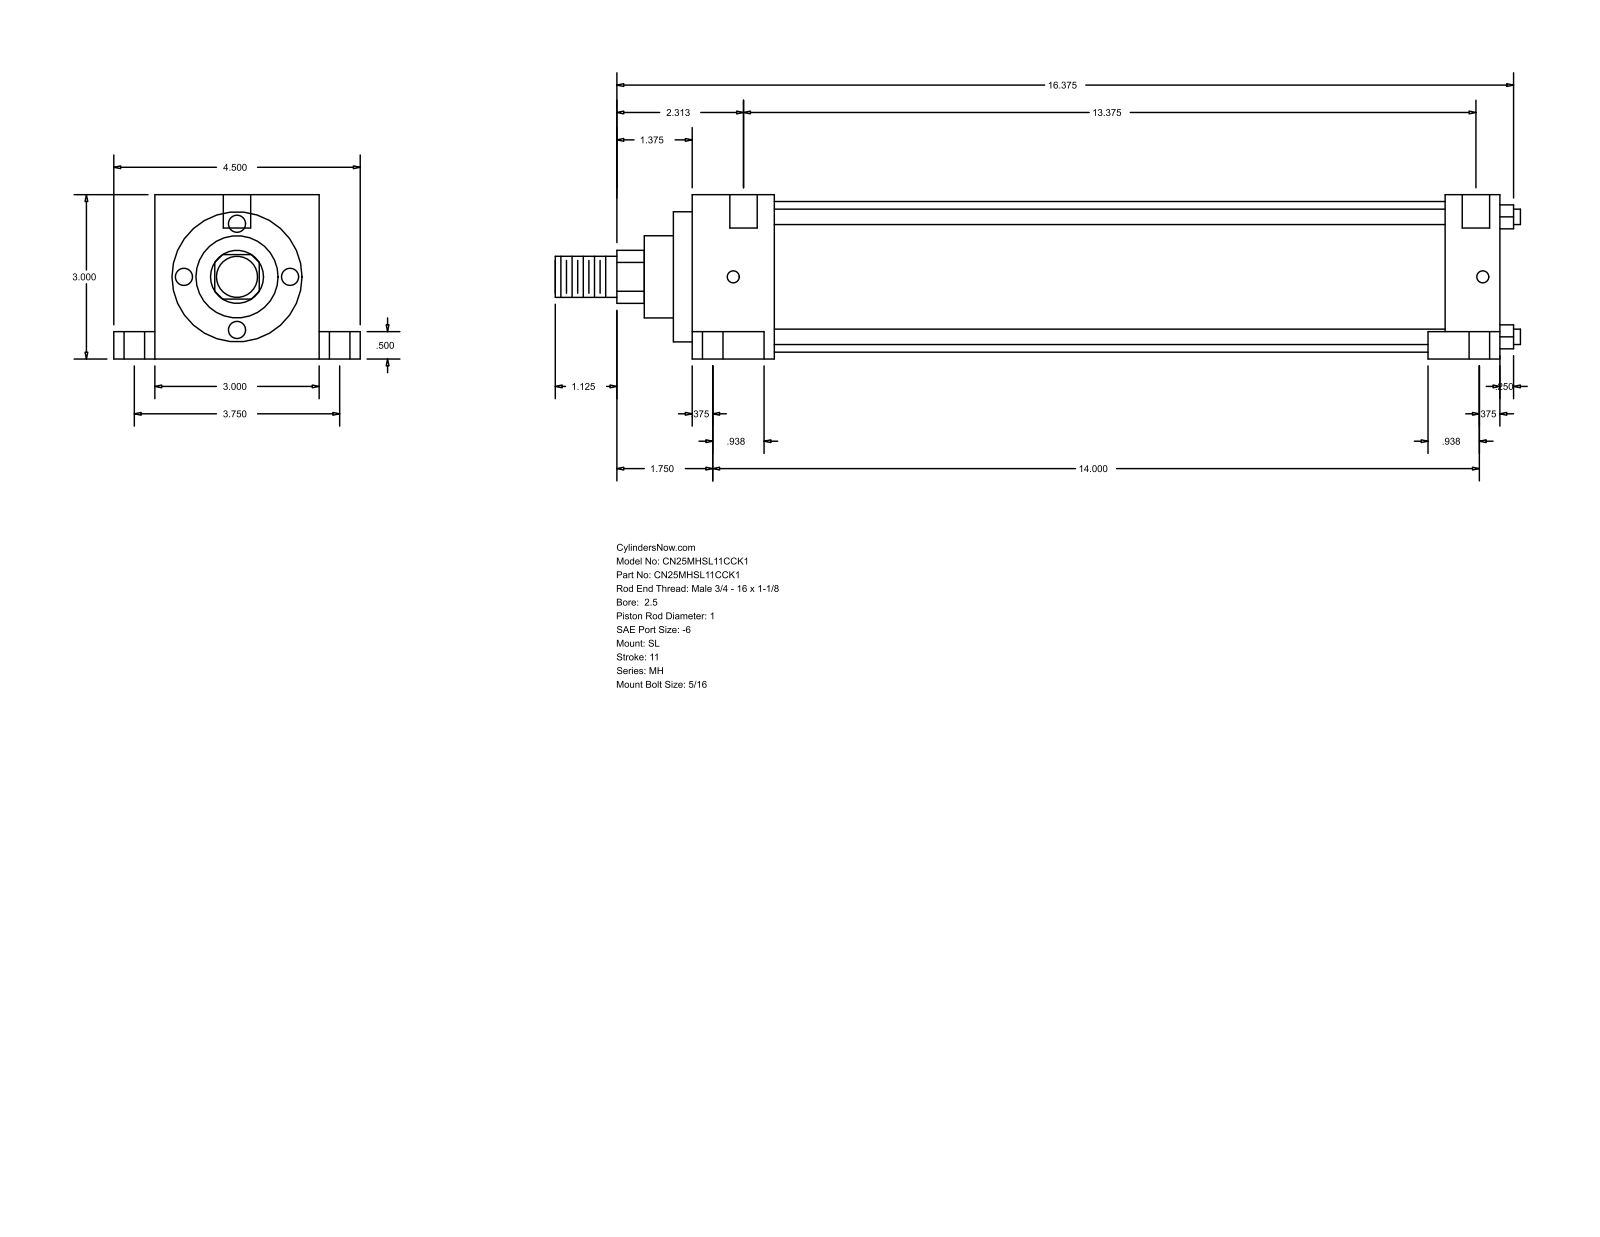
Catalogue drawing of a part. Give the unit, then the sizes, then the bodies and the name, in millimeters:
Units: millimetres
Overall size (bounding box): 447.68 × 114.3 × 76.2
Round holes (diameter × count): ⌀5.56 ×2, ⌀9.53 ×2, ⌀15.88 ×2, ⌀12.7 ×1
Round bosses / shafts (diameter × count): ⌀7.14 ×4, ⌀69.85 ×1, ⌀60.33 ×1, ⌀38.1 ×1, ⌀25.4 ×1, ⌀19.05 ×1
Partial cylindrical surfaces — rounded edges, fillets, slot ends (radius × count): R12.29 ×1
Main face-to-face distances: 76.2, 25.39, 357.99, 383.38, 12.7, 63.5, 19.05, 95.25, 13.49, 371.48
Hole centre spacings: 47.65, 3.18, 95.24
Bodies: 0 solids, 86 faces (61 planar, 25 cylindrical, 0 other)
Part name (STEP PRODUCT): MH_SL__0250_1
STEP written by: GSSL Pune (CONFIG_CONTROL_DESIGN)
